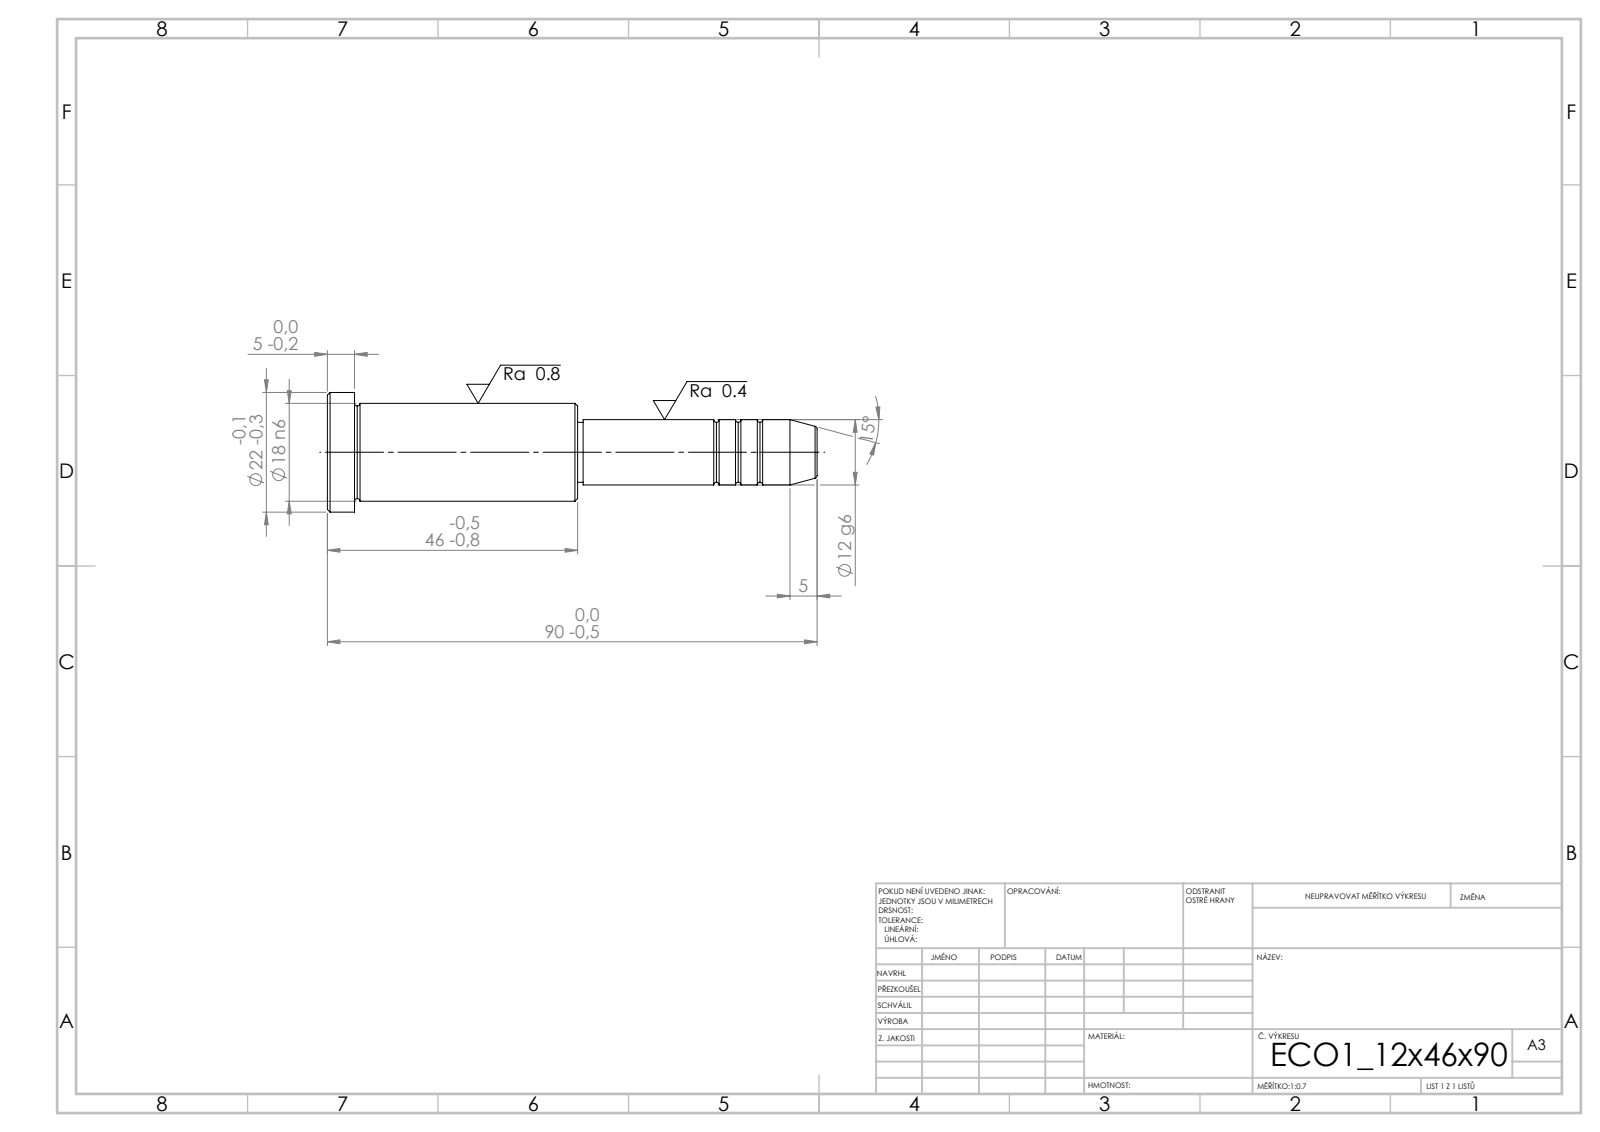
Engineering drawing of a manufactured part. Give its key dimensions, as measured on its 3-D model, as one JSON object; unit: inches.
{"step_written_by": "SolidWorks 2019 (CONFIG_CONTROL_DESIGN)", "units": "inches", "bodies": {"solids": 1, "faces": 43, "planar": 5, "cylindrical": 14, "other": 24}, "overall_size": [3.543, 0.866, 0.866], "volume_in3": 1.043, "surface_area_in2": 7.905, "round_bosses_or_shafts": [[0.866, 1], [0.709, 1], [0.472, 1], [0.433, 1]], "face_to_face_distances": [1.811, 1.614, 0.197, 1.732, 3.346, 3.543, 1.693, 0.039, 1.654, 1.85]}
